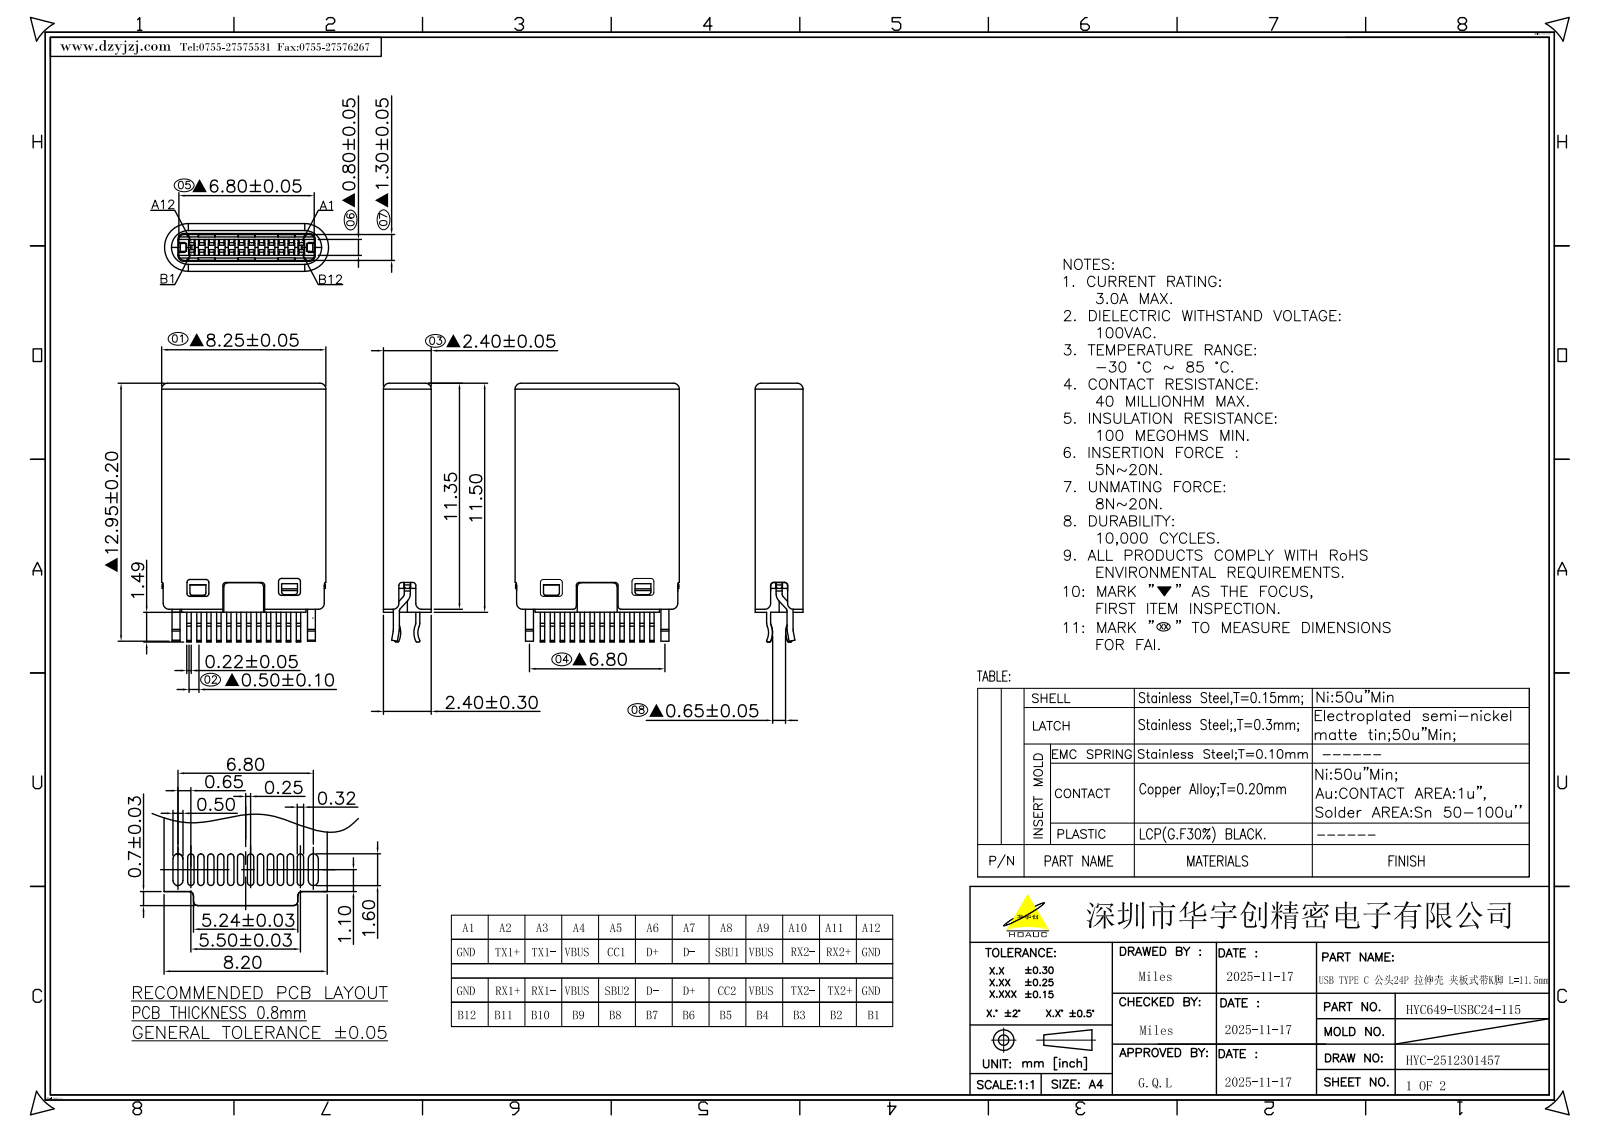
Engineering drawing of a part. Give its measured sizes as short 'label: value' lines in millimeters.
name: TANPIAN-PLASTIC_1_2__2_30
written by: CREO PARAMETRIC BY PTC INC, 2025010 (AUTOMOTIVE_DESIGN)
unit: mm
bodies: 1 solid, 891 faces (584 planar, 295 cylindrical, 12 other)
size: 13.01 × 8.25 × 2.42
volume: 170 mm³; area: 539 mm²
holes: 3× ⌀1
bosses: 1× ⌀1
rounds: 37× R0.15, 14× R0.13, 12× R0.2, 8× R0.3, 6× R0.25, 6× R1.05, 3× R0.1, 2× R0.31
face distances: 2.4, 0.8, 0.81, 0.57, 1.61, 0.79, 1.59, 1.06, 1.34, 0.53
hole spacings: 1.9, 4, 4.43
